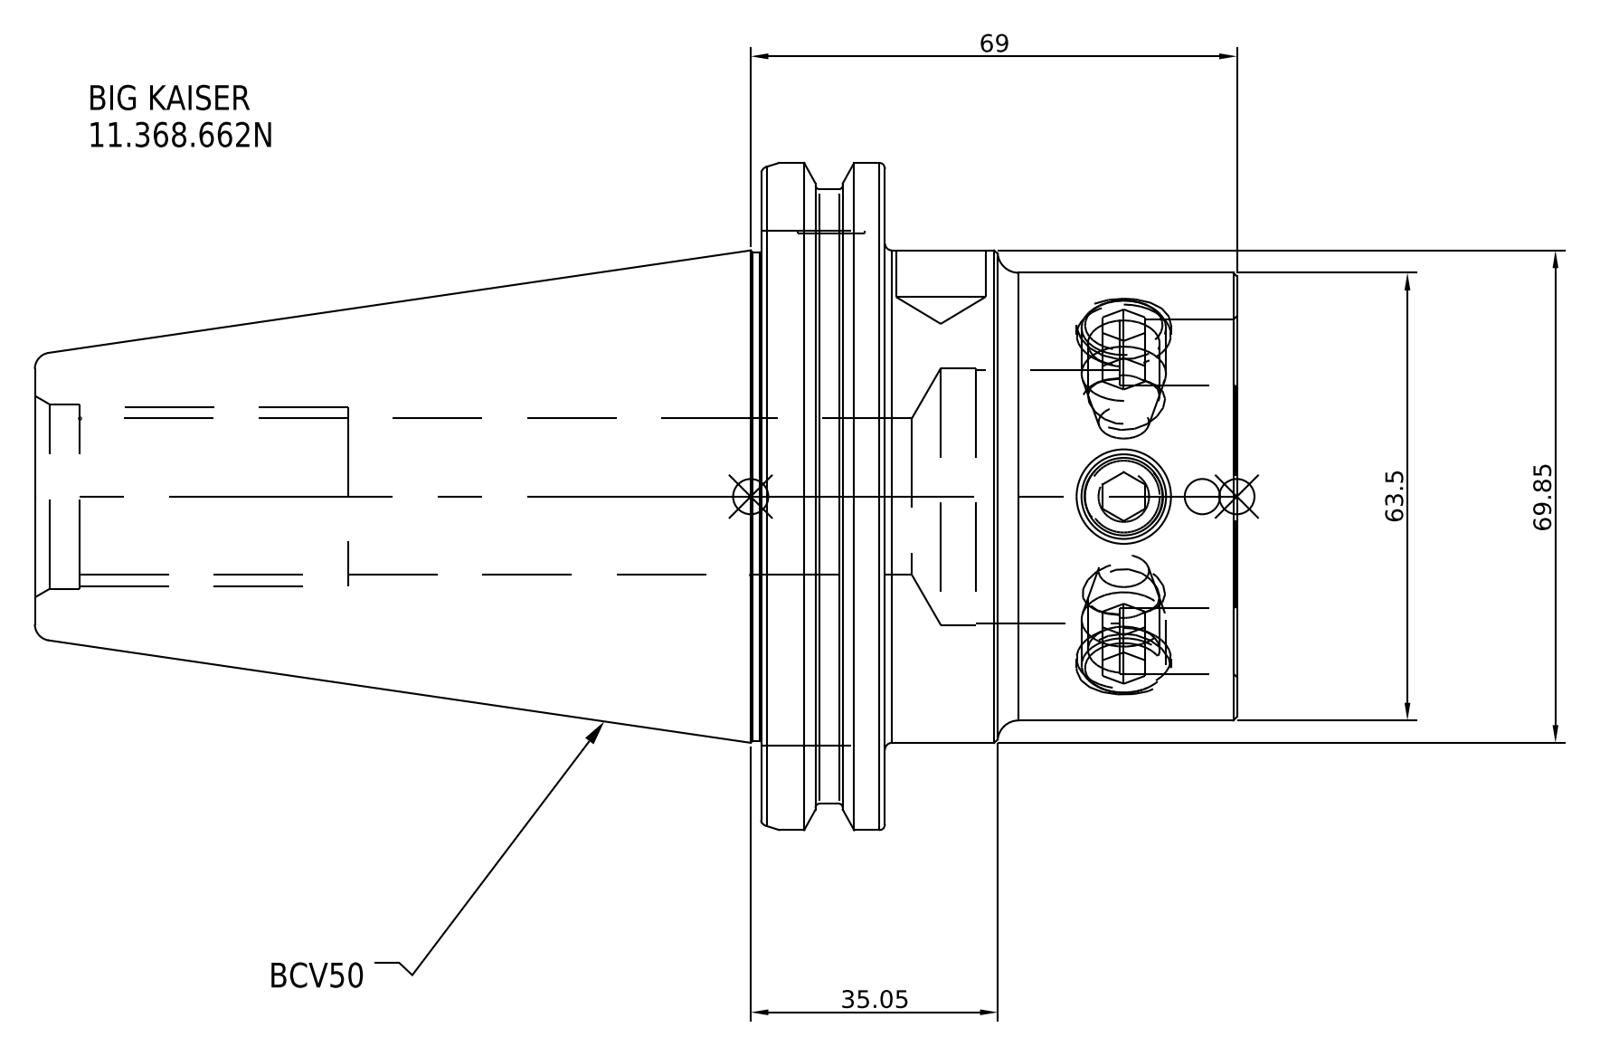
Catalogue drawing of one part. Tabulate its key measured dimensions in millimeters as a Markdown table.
| quantity | value |
| --- | --- |
| part name | 11.368.662N |
| STEP written by | SolidWorks 2021 (CONFIG_CONTROL_DESIGN) |
| units | millimeters |
| bodies | 1 solid, 16 faces (7 planar, 6 cylindrical, 3 other) |
| overall size | 170.6 × 98.43 × 98.43 |
| volume | 550 156 mm³ |
| surface area | 47 756 mm² |
| round bosses / shafts (diameter × count) | 98.43 × 1, 91.29 × 1, 69.85 × 1, 63.5 × 1 |
| main face-to-face distances | 17.55, 49.95, 67.5, 170.6, 120.65, 103.1, 34, 15.95, 33.5, 136.6 |
